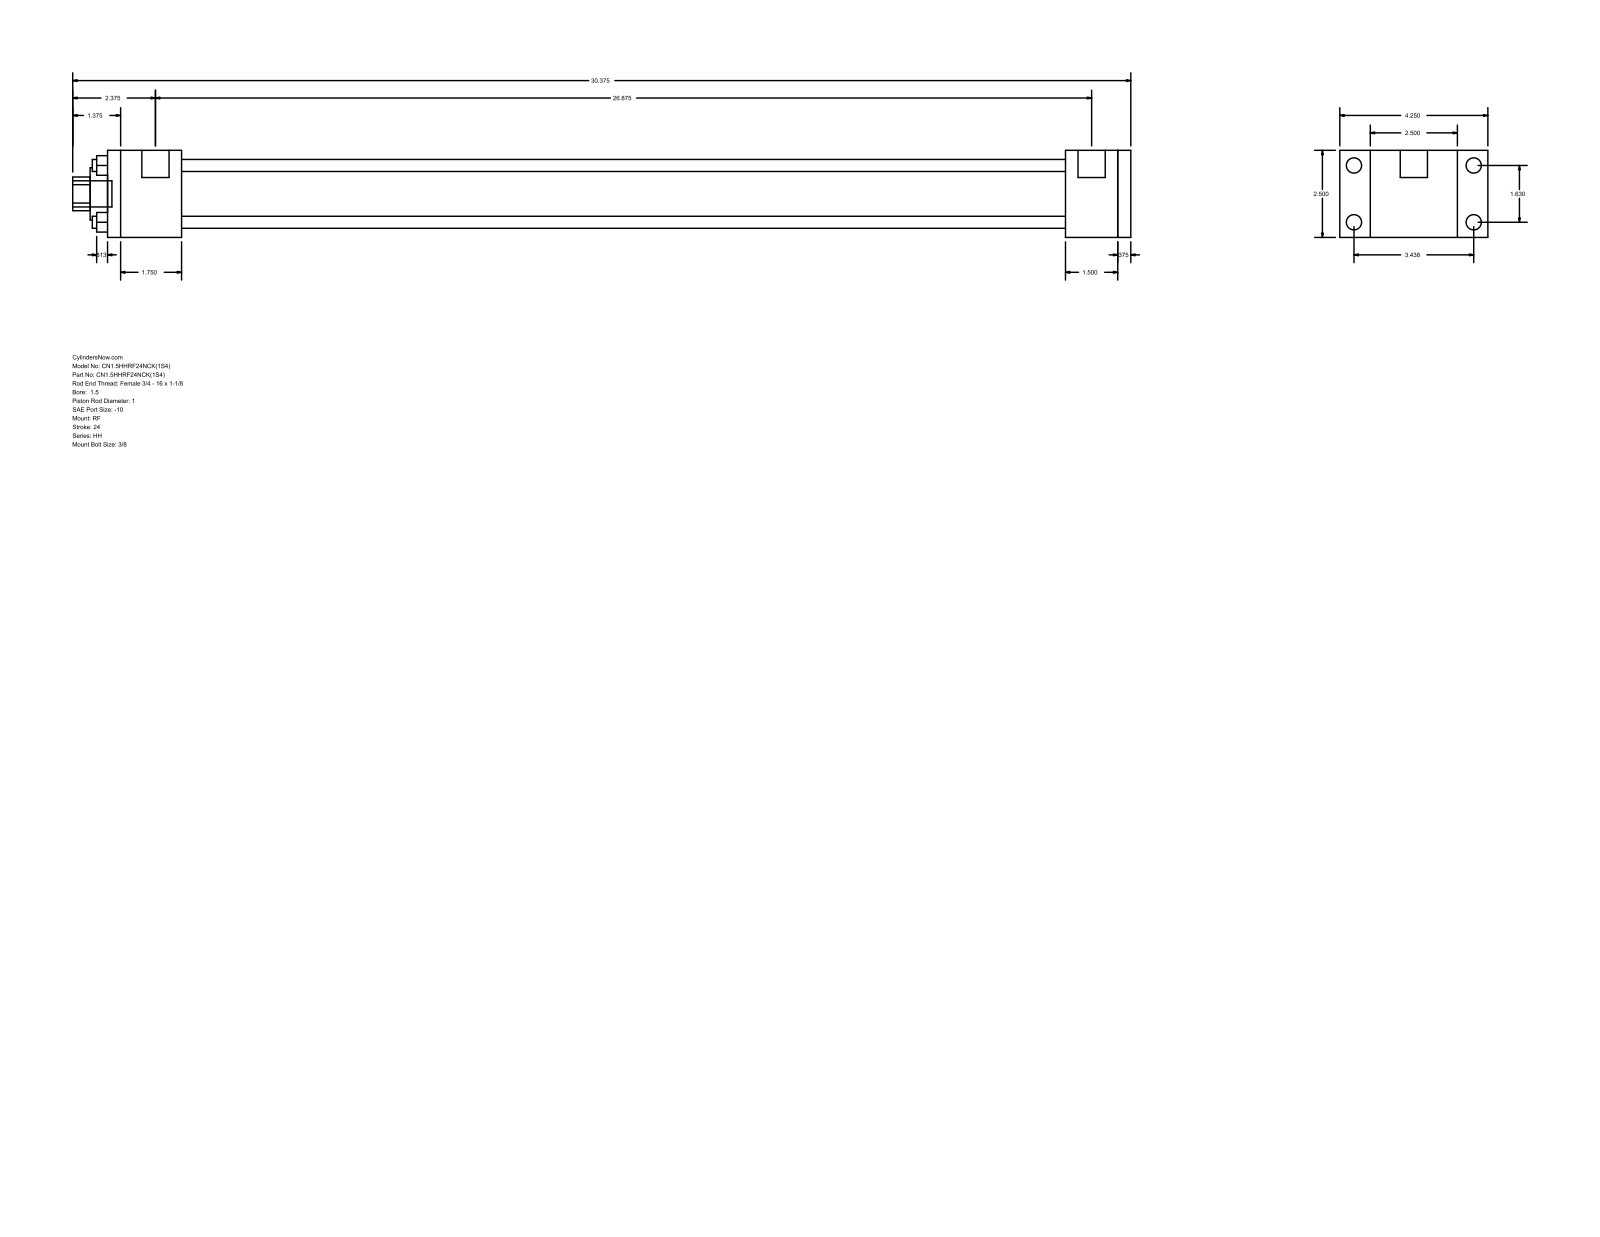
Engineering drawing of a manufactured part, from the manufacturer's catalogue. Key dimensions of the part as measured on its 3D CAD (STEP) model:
Part name (STEP PRODUCT): HH_RF__0150_1
STEP written by: GSSL Pune (CONFIG_CONTROL_DESIGN)
Units: millimetres
Bodies: 0 solids, 92 faces (64 planar, 28 cylindrical, 0 other)
Overall size (bounding box): 771.52 × 107.95 × 63.5
Round holes (diameter × count): ⌀8.76 ×4, ⌀25.4 ×1, ⌀38.1 ×1, ⌀44.45 ×1
Round bosses / shafts (diameter × count): ⌀11.13 ×4, ⌀5.56 ×4, ⌀19.84 ×2, ⌀19.05 ×1
Partial cylindrical surfaces — rounded edges, fillets, slot ends (radius × count): R12.29 ×1
Main face-to-face distances: 63.5, 9.52, 644.52, 682.62, 692.14, 38.1, 47.62, 53.98, 698.5, 736.6
Hole centre spacings: 29.27, 41.4, 58.55
